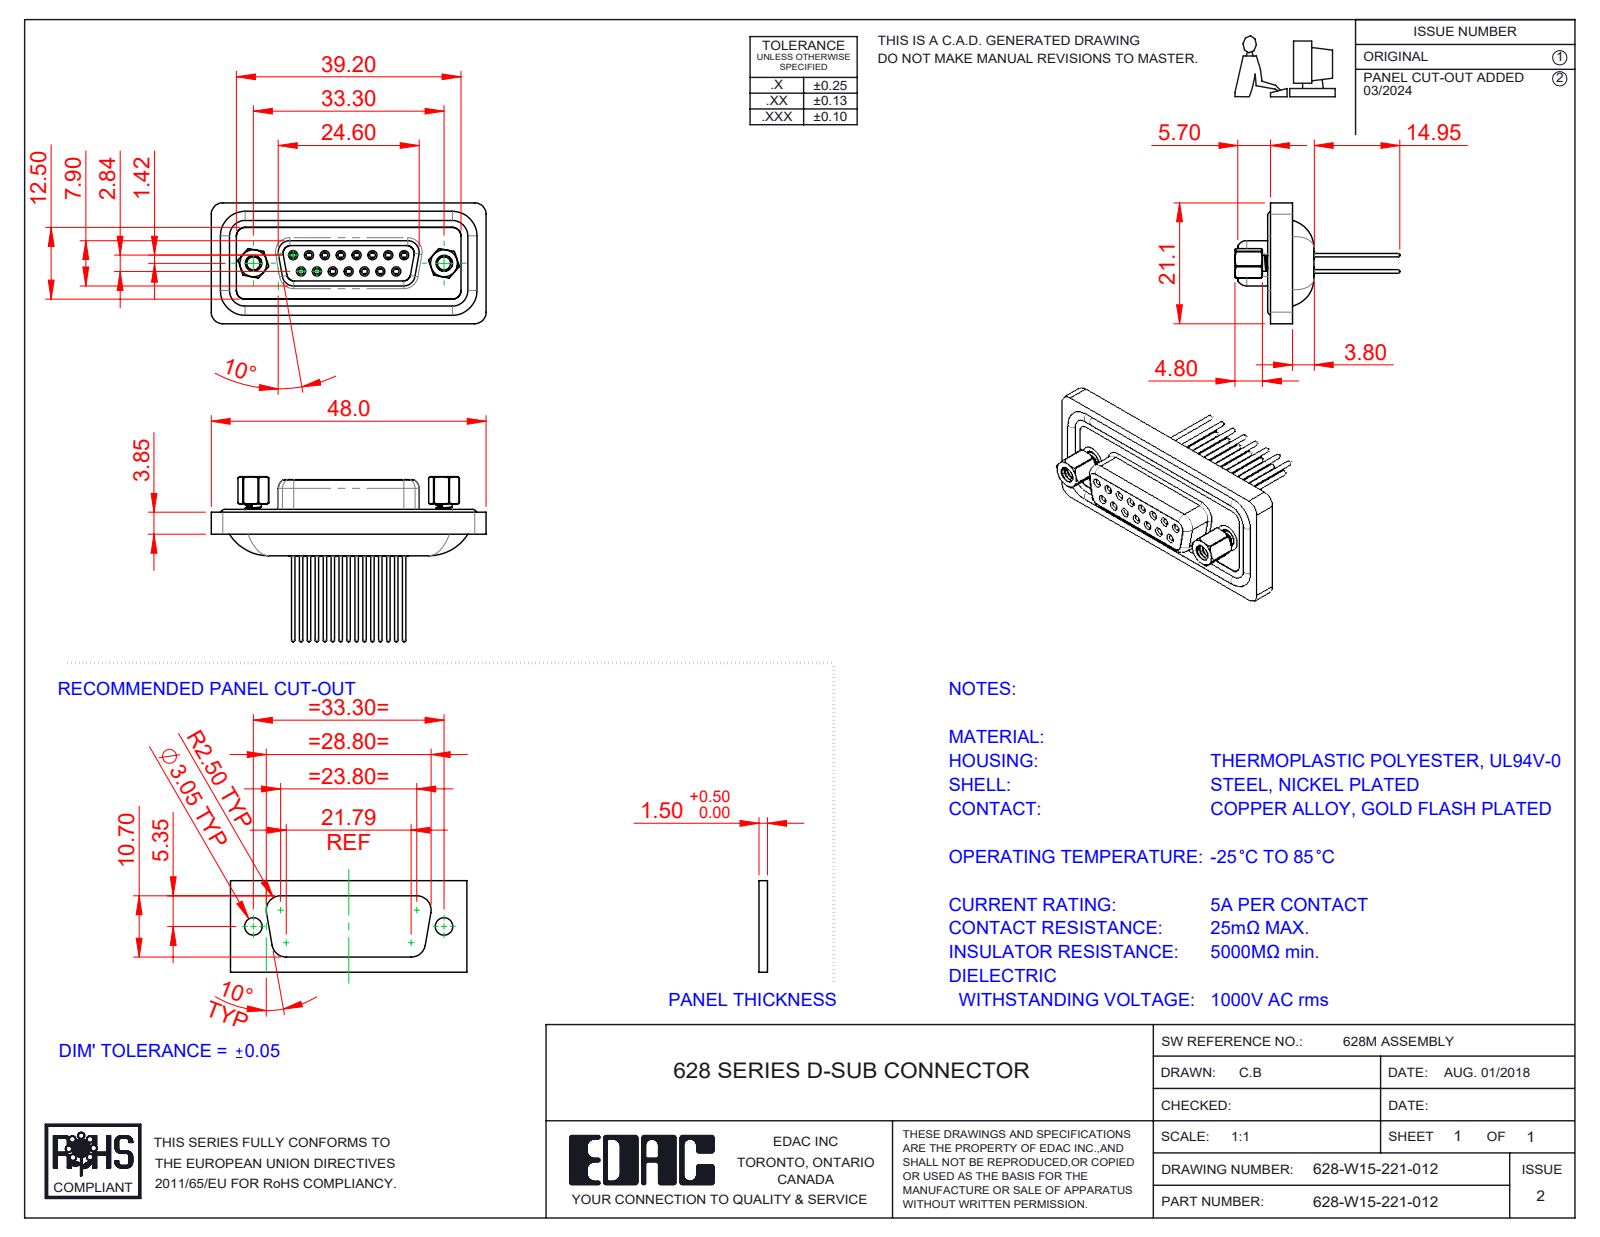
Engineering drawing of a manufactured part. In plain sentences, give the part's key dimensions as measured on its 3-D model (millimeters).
The part is named "628W 4-40 Threaded Rivet; 628W Housing_15 Contacts; 628W 4-40 Hex Standoff; 628-W15-221-012 (+4 more)". Its 3-D file was written by "SolidWorks 2020 (CONFIG_CONTROL_DESIGN)". It is 23 solids with 1278 faces: 326 planar, 535 cylindrical and 417 other. Overall it measures 48 by 28.3 by 21.1 millimeters. Its volume is 6 416 cubic millimeters and its surface area 9 985 square millimeters. Round holes: 15 of diameter 1, 15 of diameter 1.1, 15 of diameter 1.5, 15 of diameter 1.7, 15 of diameter 1.8, 15 of diameter 2, 2 of diameter 2.26, 2 of diameter 2.29, 2 of diameter 4, 2 of diameter 4.8, 2 of diameter 5. Round bosses or shafts: 19 of diameter 1.6, 15 of diameter 2.2, 15 of diameter 0.6, 7 of diameter 1.5, 2 of diameter 4.9, 2 of diameter 2.79. Partial cylindrical surfaces (rounded edges, fillets, slot ends): 16 of radius 2, 14 of radius 1.5, 8 of radius 1.35, 6 of radius 2.7, 4 of radius 0.5, 4 of radius 0.9, 4 of radius 1.6, 4 of radius 1.75. The main face-to-face distances are 0.4, 1.1, 2.75, 0.5, 3.75, 7.45, 7.5, 1, 13.65, 8.45. The hole center spacings are 3.16, 2.77, 5.54, 8.31, 5.03, 5.04, 7.48, 7.49.
